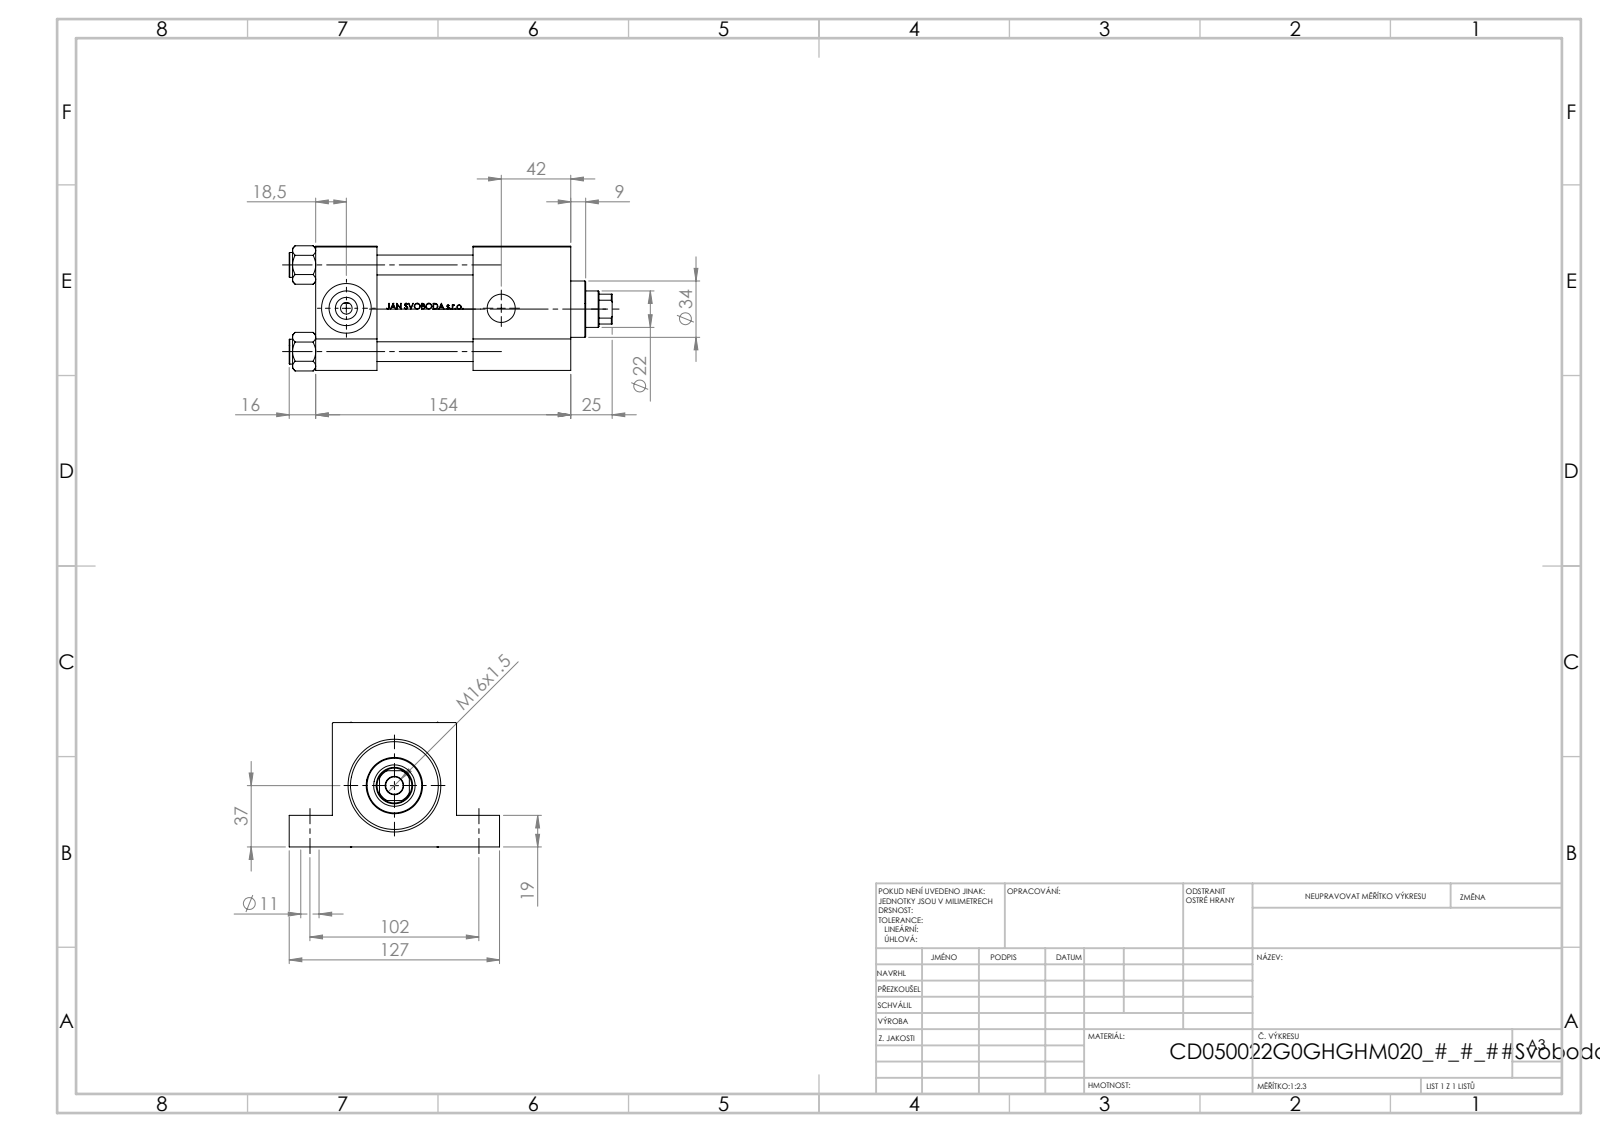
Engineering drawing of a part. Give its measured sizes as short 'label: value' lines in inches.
name: V215CD_G_Body; V215CD_G_TYCINKA; V215CD_VC_G; V215CD_VCP_G (+1 more)
written by: SolidWorks 2019 (CONFIG_CONTROL_DESIGN)
unit: in
bodies: 11 solids, 1087 faces (431 planar, 124 cylindrical, 532 other)
size: 7.677 × 5 × 2.974
volume: 46.13 in³; area: 247.3 in²
holes: 4× ⌀0.433, 4× ⌀0.472, 2× ⌀0.276, 2× ⌀0.825, 1× ⌀0.413, 1× ⌀0.669, 1× ⌀0.866, 1× ⌀0.984, 1× ⌀1.181, 1× ⌀1.614, 1× ⌀1.969, 1× ⌀2.087
bosses: 4× ⌀0.591, 1× ⌀2.205, 1× ⌀1.339
rounds: 1× R0.413
face distances: 2.953, 1.457, 6.063, 4.606, 0.748, 2.205, 3.74, 2.283, 2.323, 1.024
hole spacings: 2.059, 1.442, 1.47, 2.912, 4.016, 4.409, 5.964, 3.681
